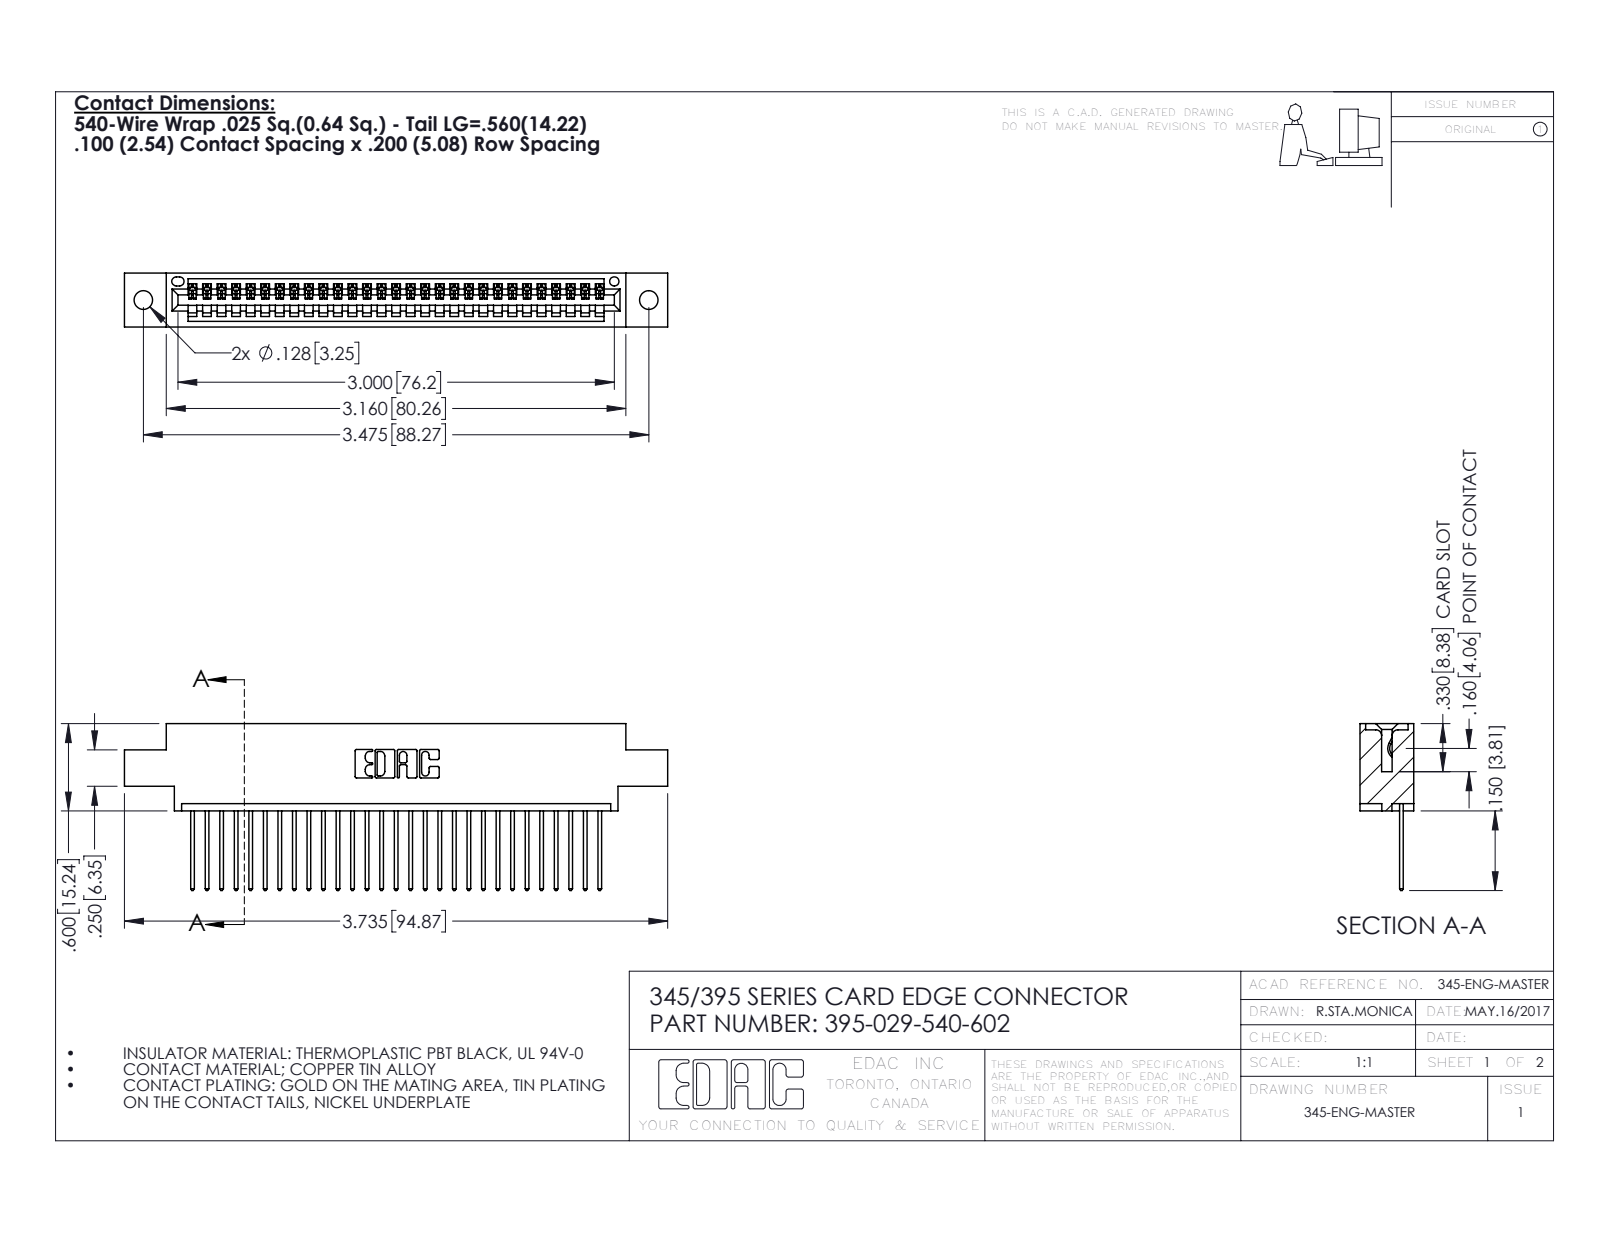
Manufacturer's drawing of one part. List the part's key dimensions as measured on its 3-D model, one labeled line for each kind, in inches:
Part name (STEP PRODUCT): 395-029-540-602; 345-292-001_345-293-140; 345 Part_0.170 Offset - 0.128 Dia
STEP written by: SolidWorks 2016 (CONFIG_CONTROL_DESIGN)
Units: inches
Bodies: 30 solids, 1812 faces (1244 planar, 568 cylindrical, 0 other)
Overall size (bounding box): 3.735 × 1.147 × 0.37
Volume: 0.537 in³ · Surface area: 18.05 in²
Round holes (diameter × count): ⌀0.128 ×2, ⌀0.064 ×1
Partial cylindrical surfaces — rounded edges, fillets, slot ends (radius × count): R0.006 ×58, R0.01 ×58, R0.01 ×22, R0.007 ×6, R0.031 ×6, R0.026 ×3, R0.031 ×2, R0.04 ×2
Main face-to-face distances: 0.298, 0.072, 0.37, 0.098, 0.272, 0.025, 0.2, 0.225, 0.175, 0.149
Hole centre spacings: 0.27, 3.24, 3.475
